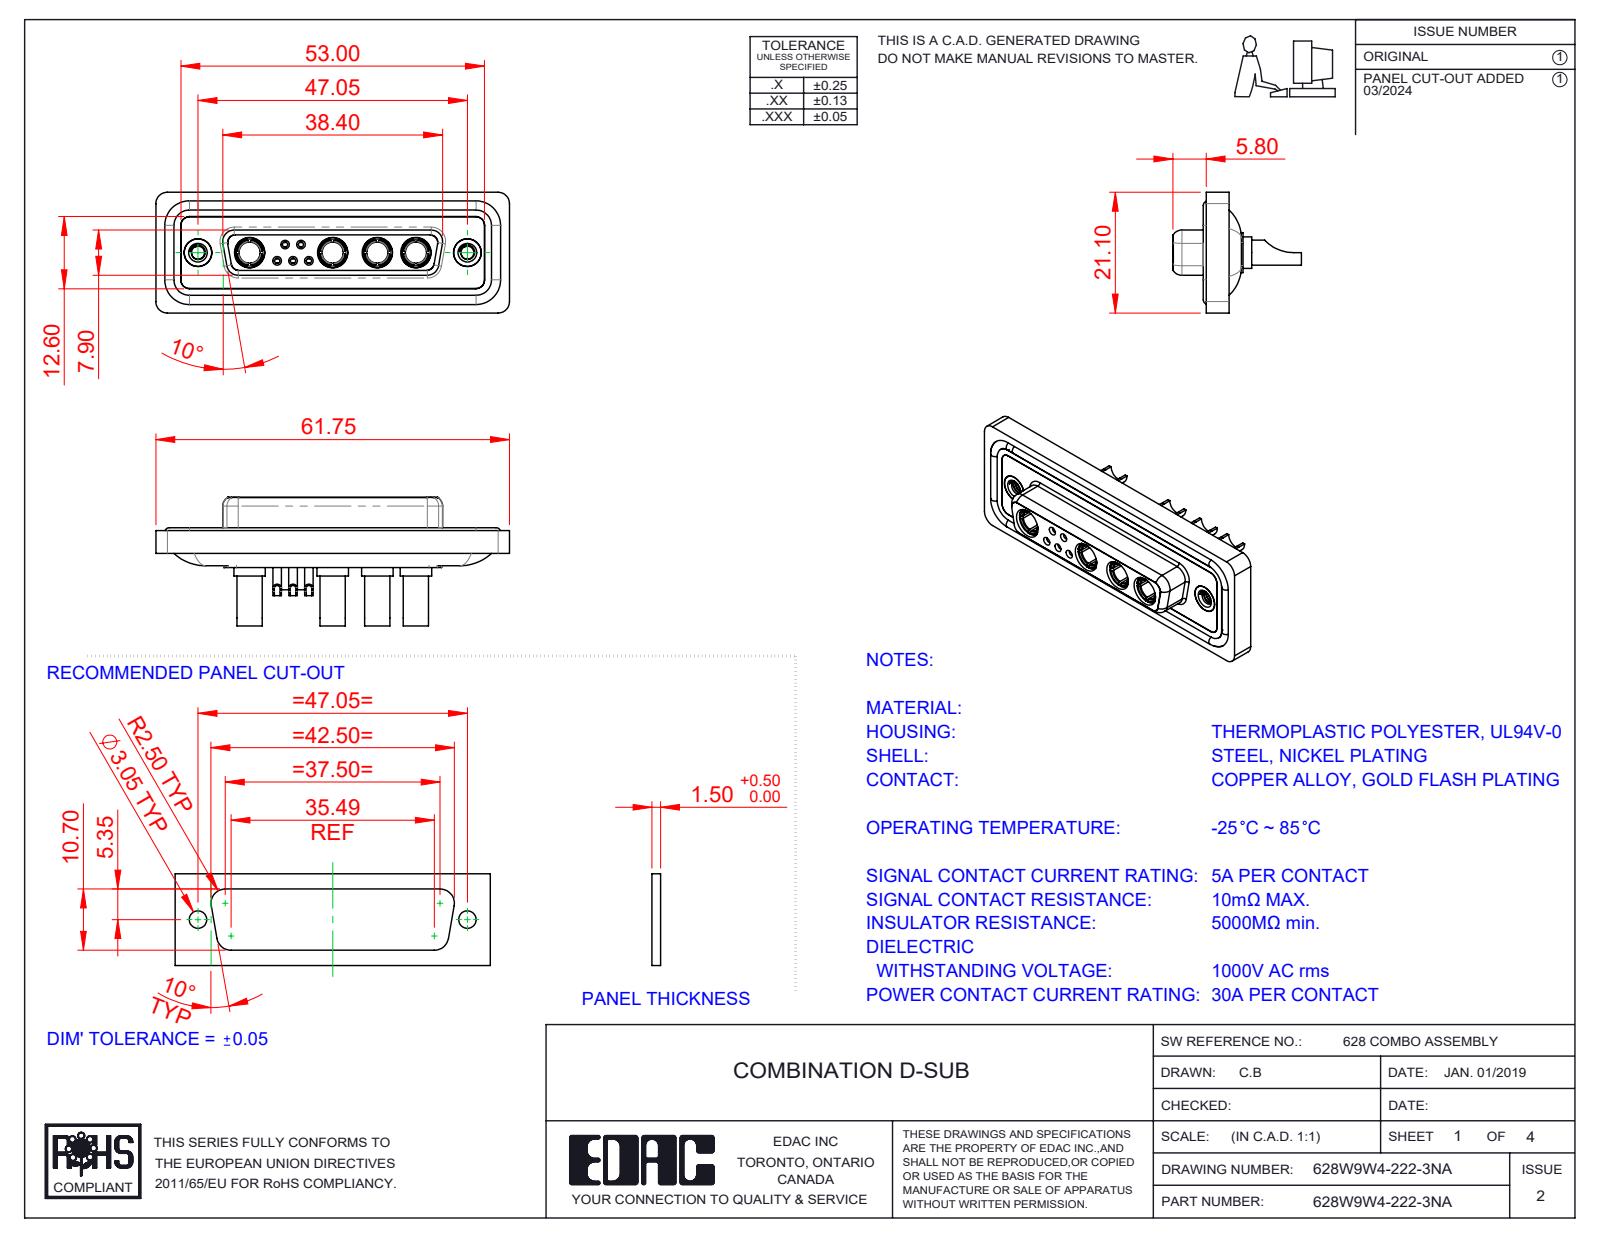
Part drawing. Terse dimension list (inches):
name: Power Socket_30A SC; 628Combo Housing_9W4; 628Combo Shell Front_25 Contacts; 628Combo Contact Row 2_22 (+5 more)
written by: SolidWorks 2023 (CONFIG_CONTROL_DESIGN)
unit: in
bodies: 20 solids, 979 faces (318 planar, 399 cylindrical, 262 other)
size: 2.431 × 0.884 × 0.831
volume: 0.508 in³; area: 21.77 in²
holes: 6× ⌀0.191, 5× ⌀0.035, 5× ⌀0.039, 5× ⌀0.043, 5× ⌀0.059, 5× ⌀0.079, 4× ⌀0.138, 4× ⌀0.146, 4× ⌀0.209, 3× ⌀0.063, 2× ⌀0.067, 2× ⌀0.089
bosses: 6× ⌀0.063, 5× ⌀0.087, 4× ⌀0.217, 4× ⌀0.205, 4× ⌀0.195, 4× ⌀0.187, 4× ⌀0.173, 4× ⌀0.148
rounds: 22× R0.059, 18× R0.079, 8× R0.053, 8× R0.063, 6× R0.039, 4× R0.01, 4× R0.02, 4× R0.024
face distances: 0.016, 0.071, 0.293, 0.222, 0.02, 0.278, 0.26, 0.063, 0.043, 0.114
hole spacings: 0.124, 0.109, 0.198, 0.109, 0.173, 0.198, 0.218, 0.226
